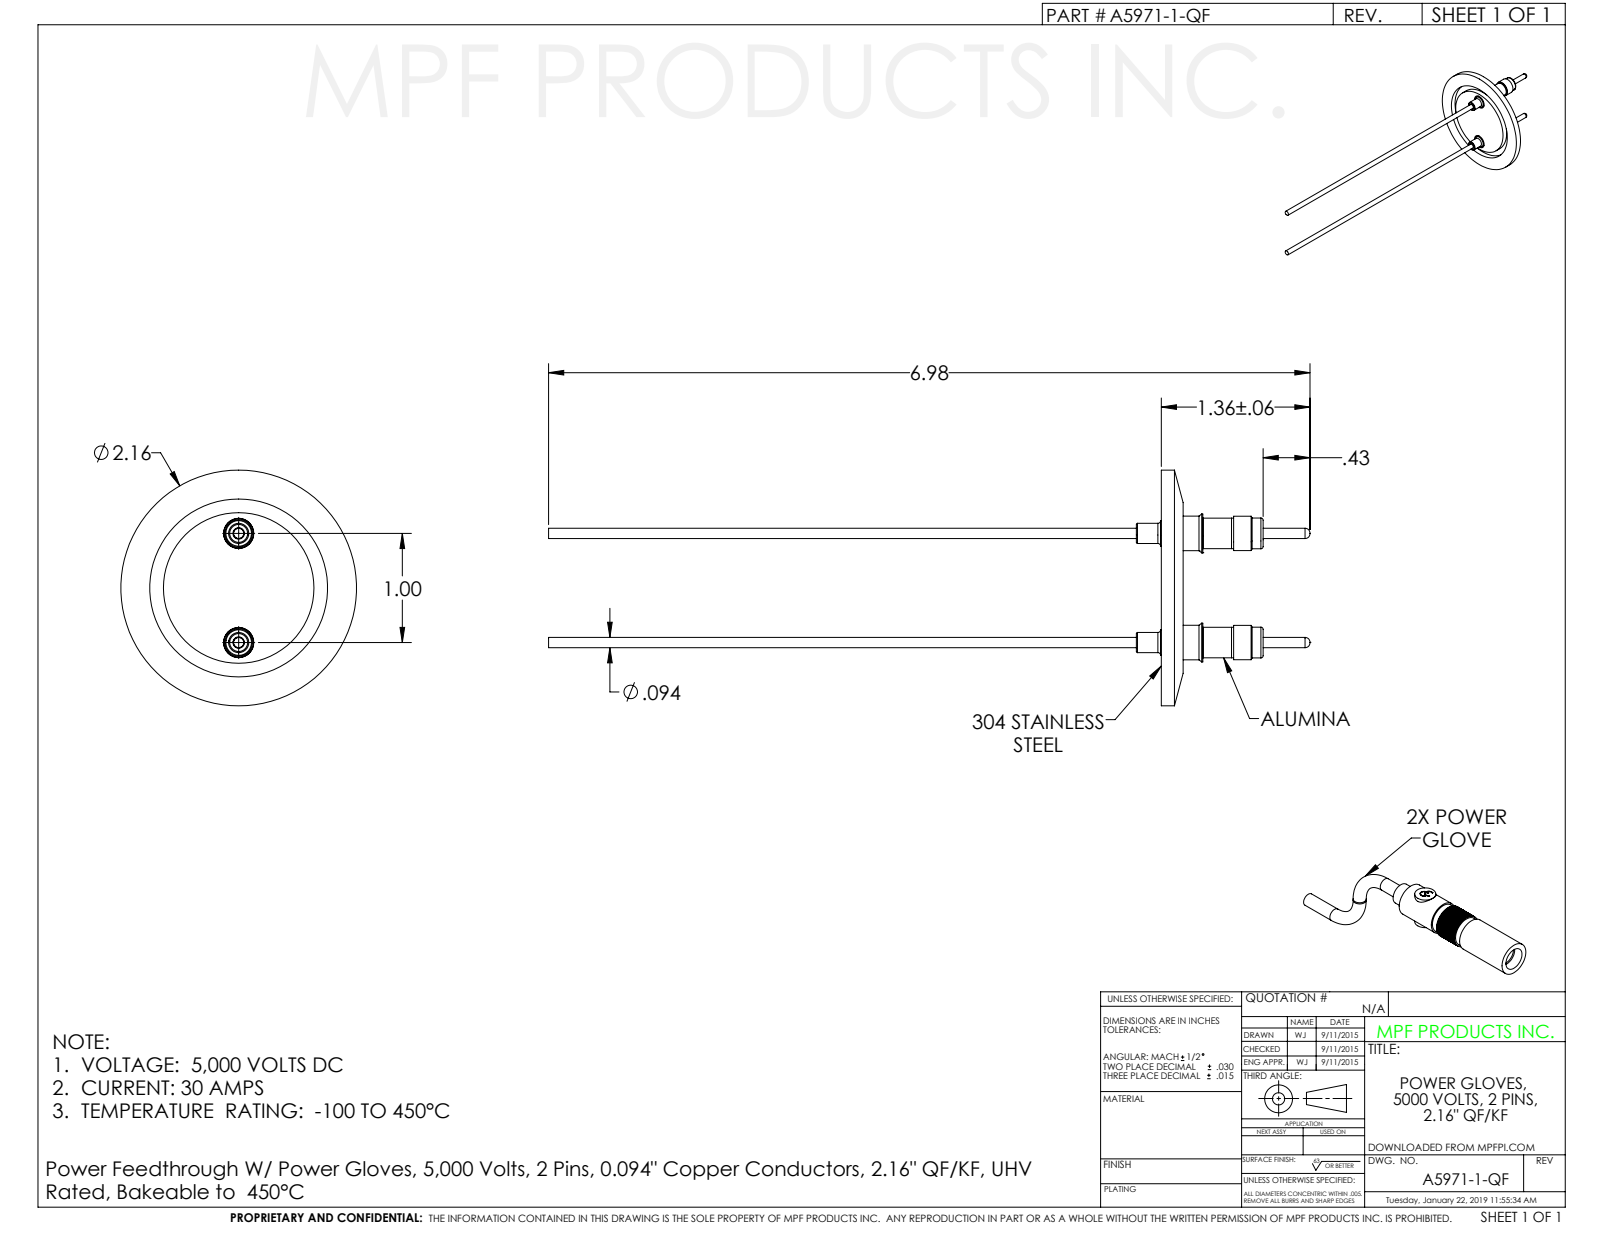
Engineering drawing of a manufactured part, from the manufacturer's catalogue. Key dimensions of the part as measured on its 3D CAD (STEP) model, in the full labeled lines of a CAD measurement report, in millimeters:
Part name (STEP PRODUCT): A5971-1-QF
STEP written by: SolidWorks 2012 (CONFIG_CONTROL_DESIGN)
Units: millimetres
Bodies: 1 solid, 132 faces (24 planar, 66 cylindrical, 42 other)
Overall size (bounding box): 177.3 × 54.9 × 54.9
Volume: 13 500 mm³ · Surface area: 10 810 mm²
Round holes (diameter × count): ⌀2.7 ×2, ⌀6.5 ×2, ⌀6.6 ×2, ⌀7 ×2, ⌀7 ×2, ⌀41.4 ×1
Round bosses / shafts (diameter × count): ⌀7.9 ×2, ⌀7.9 ×2, ⌀7.3 ×2, ⌀7.2 ×2, ⌀7.1 ×2, ⌀6.2 ×2, ⌀6 ×2, ⌀2.4 ×2
Main face-to-face distances: 5.1, 2.5, 23.7, 21.2, 18.7, 20.2, 17.7, 15.1, 3.6, 1.4
Hole centre spacings: 12.7, 25.4
